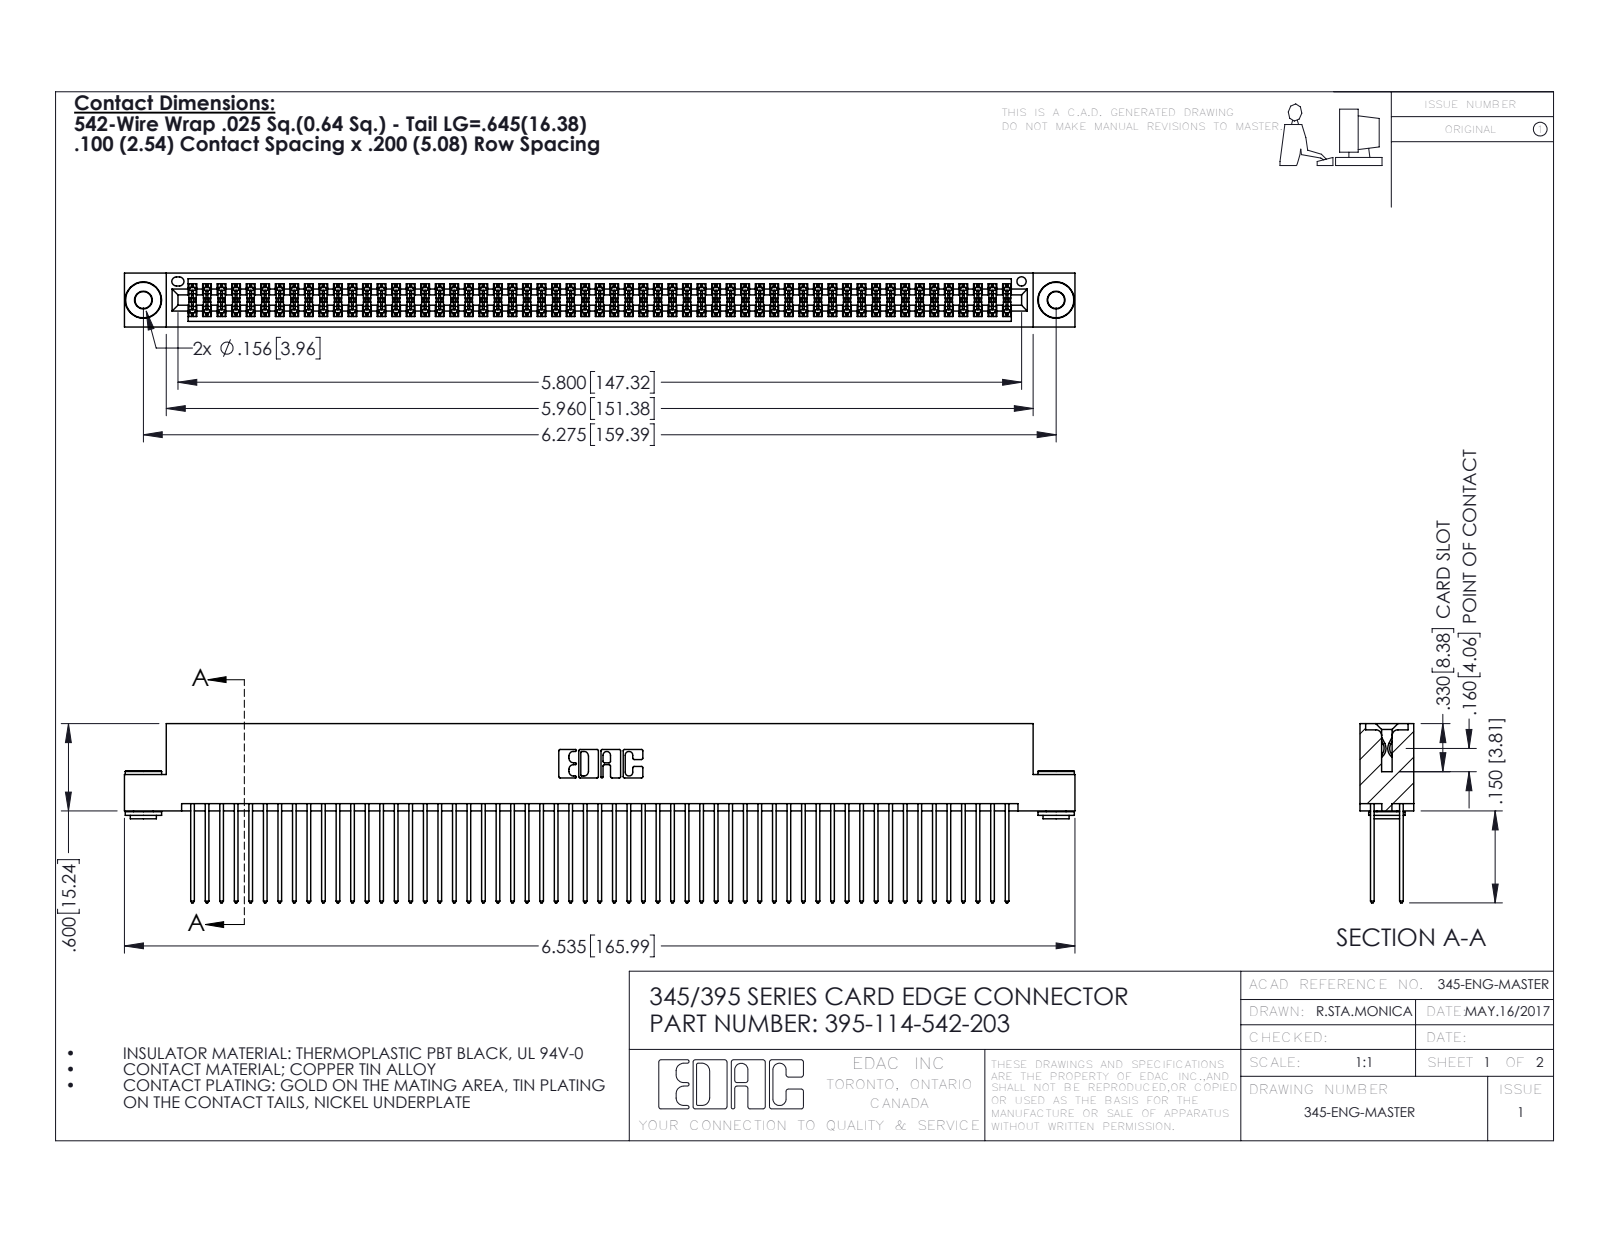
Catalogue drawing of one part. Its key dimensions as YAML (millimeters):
part_name: "345 Part_Flush Mounting Lugs - 0.156 Dia-TH; 395-114-542-203; 345-250-002_345-250-002-102; 345-292-001_345-293-142"
step_written_by: "SolidWorks 2016 (CONFIG_CONTROL_DESIGN)"
units: millimeters
bodies: {solids: 117, faces: 5864, planar: 3852, cylindrical: 2004, other: 8}
overall_size: [166, 31.3, 9.4]
volume: 16810
surface_area: 27830
round_holes:
  - {diameter: 2.9, count: 2}
  - {diameter: 4, count: 2}
  - {diameter: 1.6, count: 1}
round_bosses_or_shafts:
  - {diameter: 6.4, count: 2}
  - {diameter: 4.6, count: 2}
  - {diameter: 3.5, count: 2}
partial_cylinders:
  - {radius: 0.2, count: 171}
  - {radius: 0.3, count: 114}
  - {radius: 0.3, count: 22}
  - {radius: 0.2, count: 6}
  - {radius: 0.8, count: 6}
  - {radius: 0.7, count: 3}
  - {radius: 0.4, count: 2}
  - {radius: 0.5, count: 2}
face_to_face_distances: [1.8, 7.6, 5.1, 0.6, 2.5, 6.9, 5.7, 9.4, 4.4, 3.8]
hole_center_spacings: [6.9, 153.4, 159.4]
